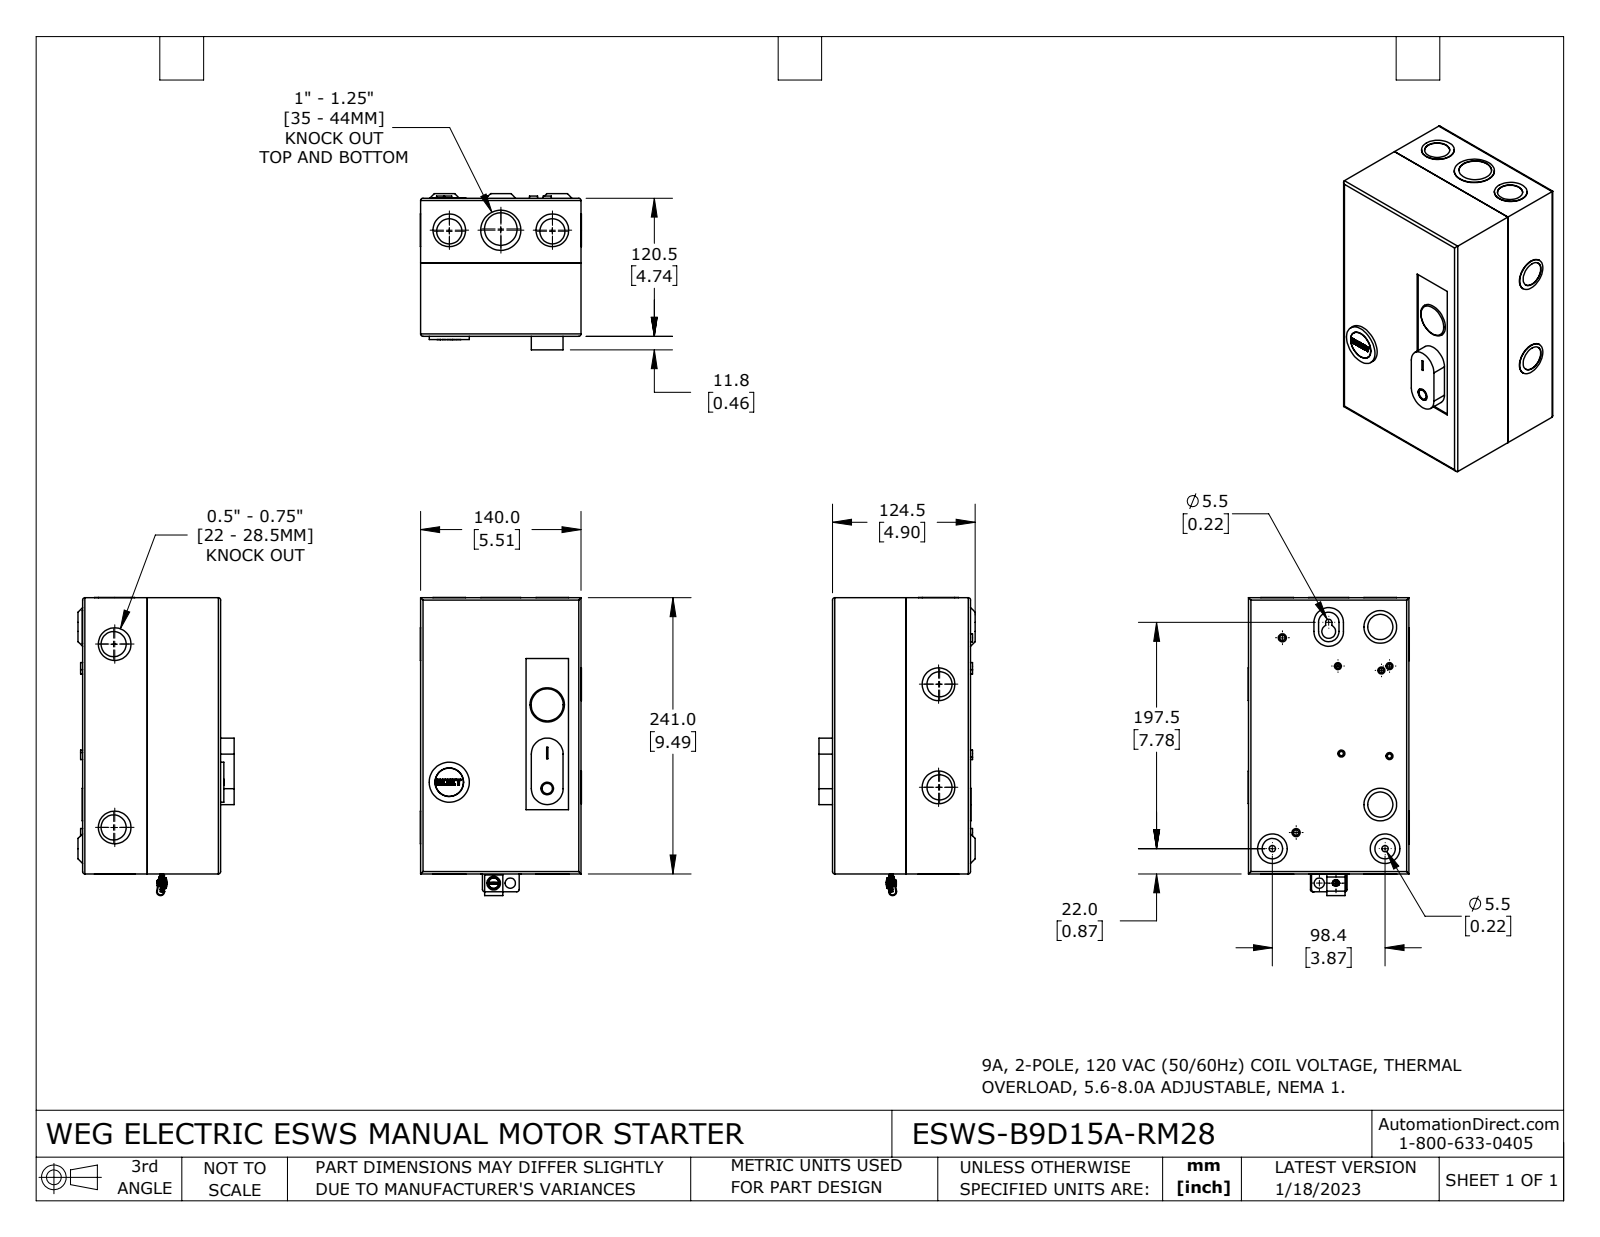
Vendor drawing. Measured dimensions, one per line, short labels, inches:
name: ESWS-B9D15A-RM28
written by: SolidWorks 2021 (CONFIG_CONTROL_DESIGN)
unit: in
bodies: 7 solids, 435 faces (168 planar, 230 cylindrical, 37 other)
size: 10.248 × 5.535 × 5.366
volume: 16.23 in³; area: 585.2 in²
holes: 5× ⌀0.146, 4× ⌀0.864, 2× ⌀0.183, 2× ⌀0.217, 2× ⌀0.354, 2× ⌀0.864, 2× ⌀0.866, 2× ⌀0.886, 1× ⌀0.256, 1× ⌀0.303, 1× ⌀0.433, 1× ⌀0.469
bosses: 6× ⌀1.124, 5× ⌀0.24, 2× ⌀1.122, 2× ⌀0.278, 1× ⌀1.38, 1× ⌀1.378, 1× ⌀1.193, 1× ⌀1.148
rounds: 34× R0.004, 13× R0.079, 4× R0.031, 3× R0.108, 2× R0.059, 2× R0.075, 2× R0.122, 2× R0.138
face distances: 0.047, 4.697, 5.465, 4.65, 9.441, 4.744, 5.417, 5.512, 0.071, 0.063
hole spacings: 0.571, 1.378, 1.773, 3.387, 3.543, 4.921, 5.995, 7.484
